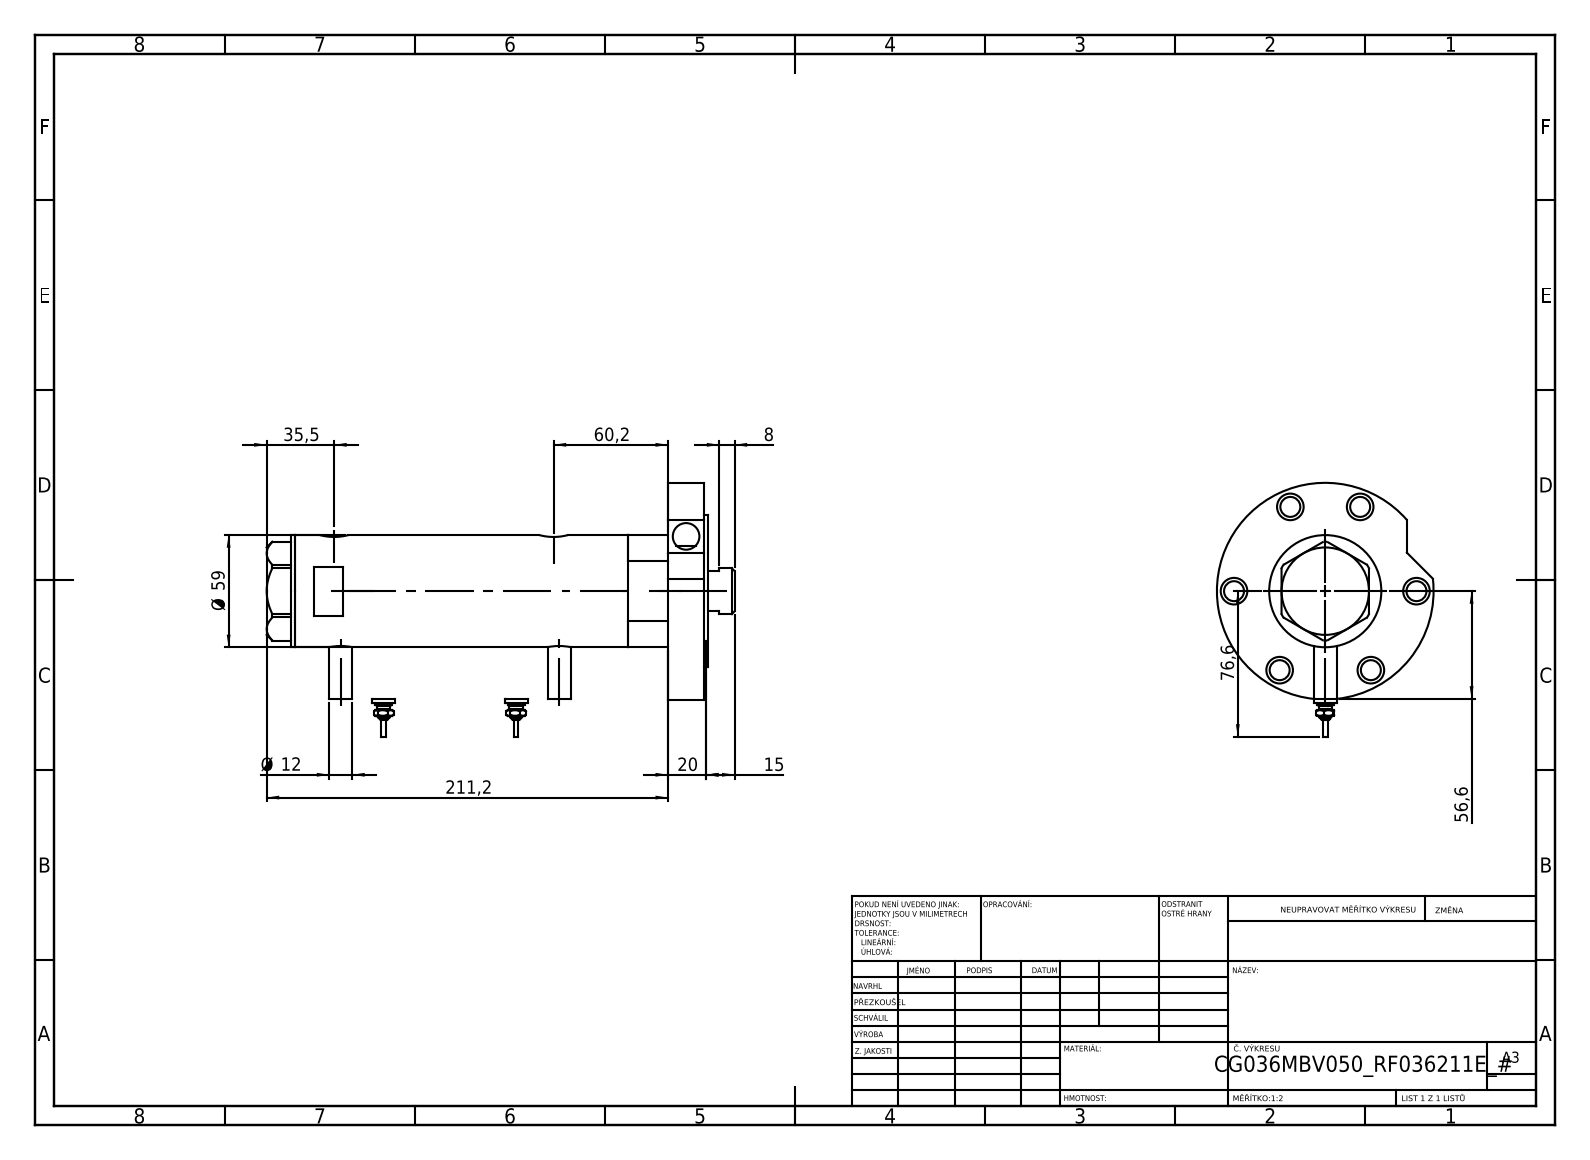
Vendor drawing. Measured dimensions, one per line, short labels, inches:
name: V270CG_MIDDLE; V270CG_RF211E; Switch; V270CG_FRONT (+2 more)
written by: SolidWorks 2019 (CONFIG_CONTROL_DESIGN)
unit: in
bodies: 7 solids, 256 faces (90 planar, 102 cylindrical, 64 other)
size: 9.693 × 5.26 × 4.488
volume: 43.71 in³; area: 233.5 in²
holes: 7× ⌀0.551, 6× ⌀0.413, 2× ⌀0.383, 2× ⌀0.492, 2× ⌀0.591, 1× ⌀0.335, 1× ⌀0.984, 1× ⌀1.043, 1× ⌀1.417, 1× ⌀1.575, 1× ⌀1.89, 1× ⌀2.047
bosses: 4× ⌀0.472, 2× ⌀0.354, 2× ⌀0.276, 2× ⌀0.177, 2× ⌀0.098, 1× ⌀4.488, 1× ⌀3.15, 1× ⌀2.323
face distances: 0.079, 0.748, 0.827, 8.551, 7.724, 8.472, 5.402, 2.323, 3.071, 3.15
hole spacings: 1.89, 2.1, 3.143, 3.273, 3.39, 3.772, 0.114, 0.138
